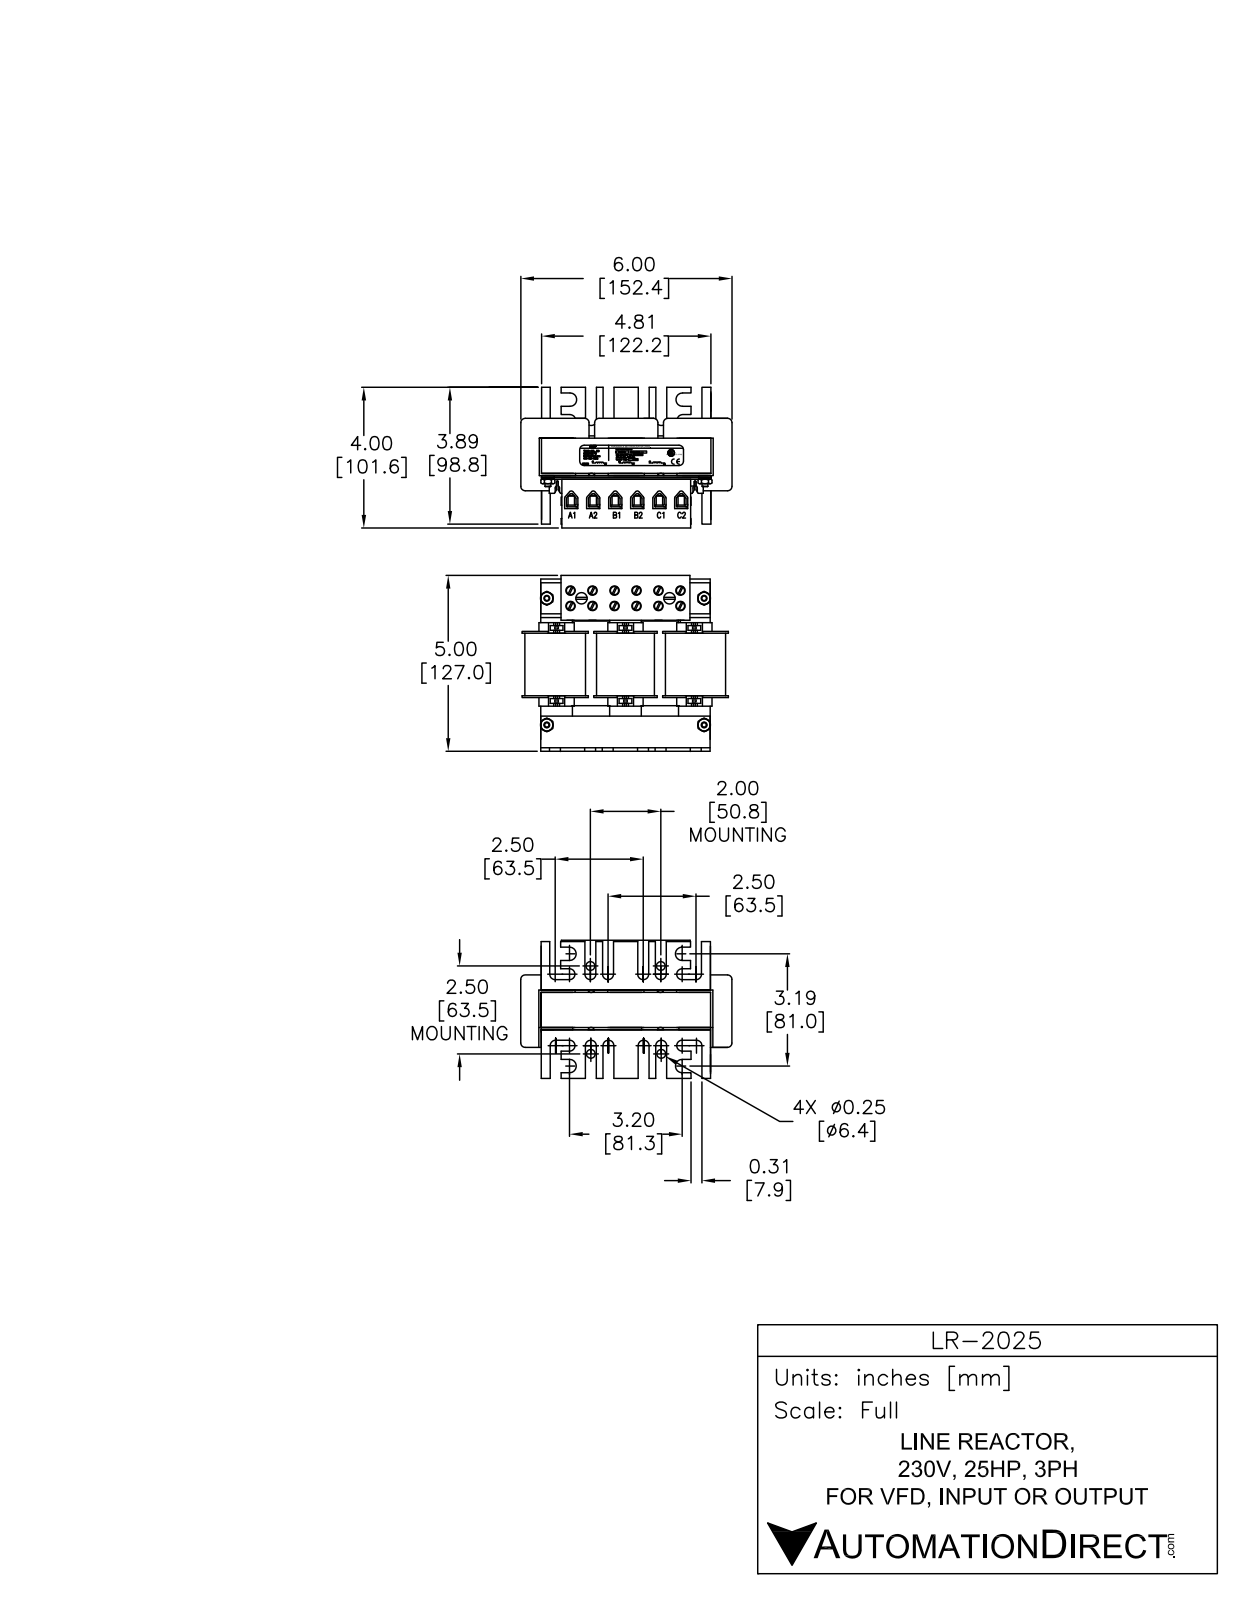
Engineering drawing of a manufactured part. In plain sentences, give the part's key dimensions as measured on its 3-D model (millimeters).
The part is named "LR-2025". Its 3-D file was written by "SolidWorks 2011 (AUTOMOTIVE_DESIGN)". It is 35 solids with 1497 faces: 868 planar, 491 cylindrical and 138 other. Overall it measures 178.25 by 144.95 by 121.72 millimeters. Its volume is 1 152 000 cubic millimeters and its surface area 208 207 square millimeters. Round holes: 12 of diameter 6.8, 12 of diameter 8.62, 5 of diameter 7.25. Round bosses or shafts: 20 of diameter 6.8, 12 of diameter 10.25, 5 of diameter 12, 5 of diameter 10.5, 2 of diameter 4.66, 1 of diameter 4.67, 1 of diameter 4.65, 1 of diameter 4.65. Partial cylindrical surfaces (rounded edges, fillets, slot ends): 130 of radius 0.75, 12 of radius 1, 12 of radius 5, 12 of radius 7, 6 of radius 2.25, 5 of radius 4.71, 4 of radius 1.5, 4 of radius 4.88. The main face-to-face distances are 2, 62, 12.25, 47.25, 45.25, 4.75, 2.75, 60, 14.25, 33. The hole center spacings are 16, 32, 11.27, 48, 22.45, 11.14, 15.69, 15.75.
